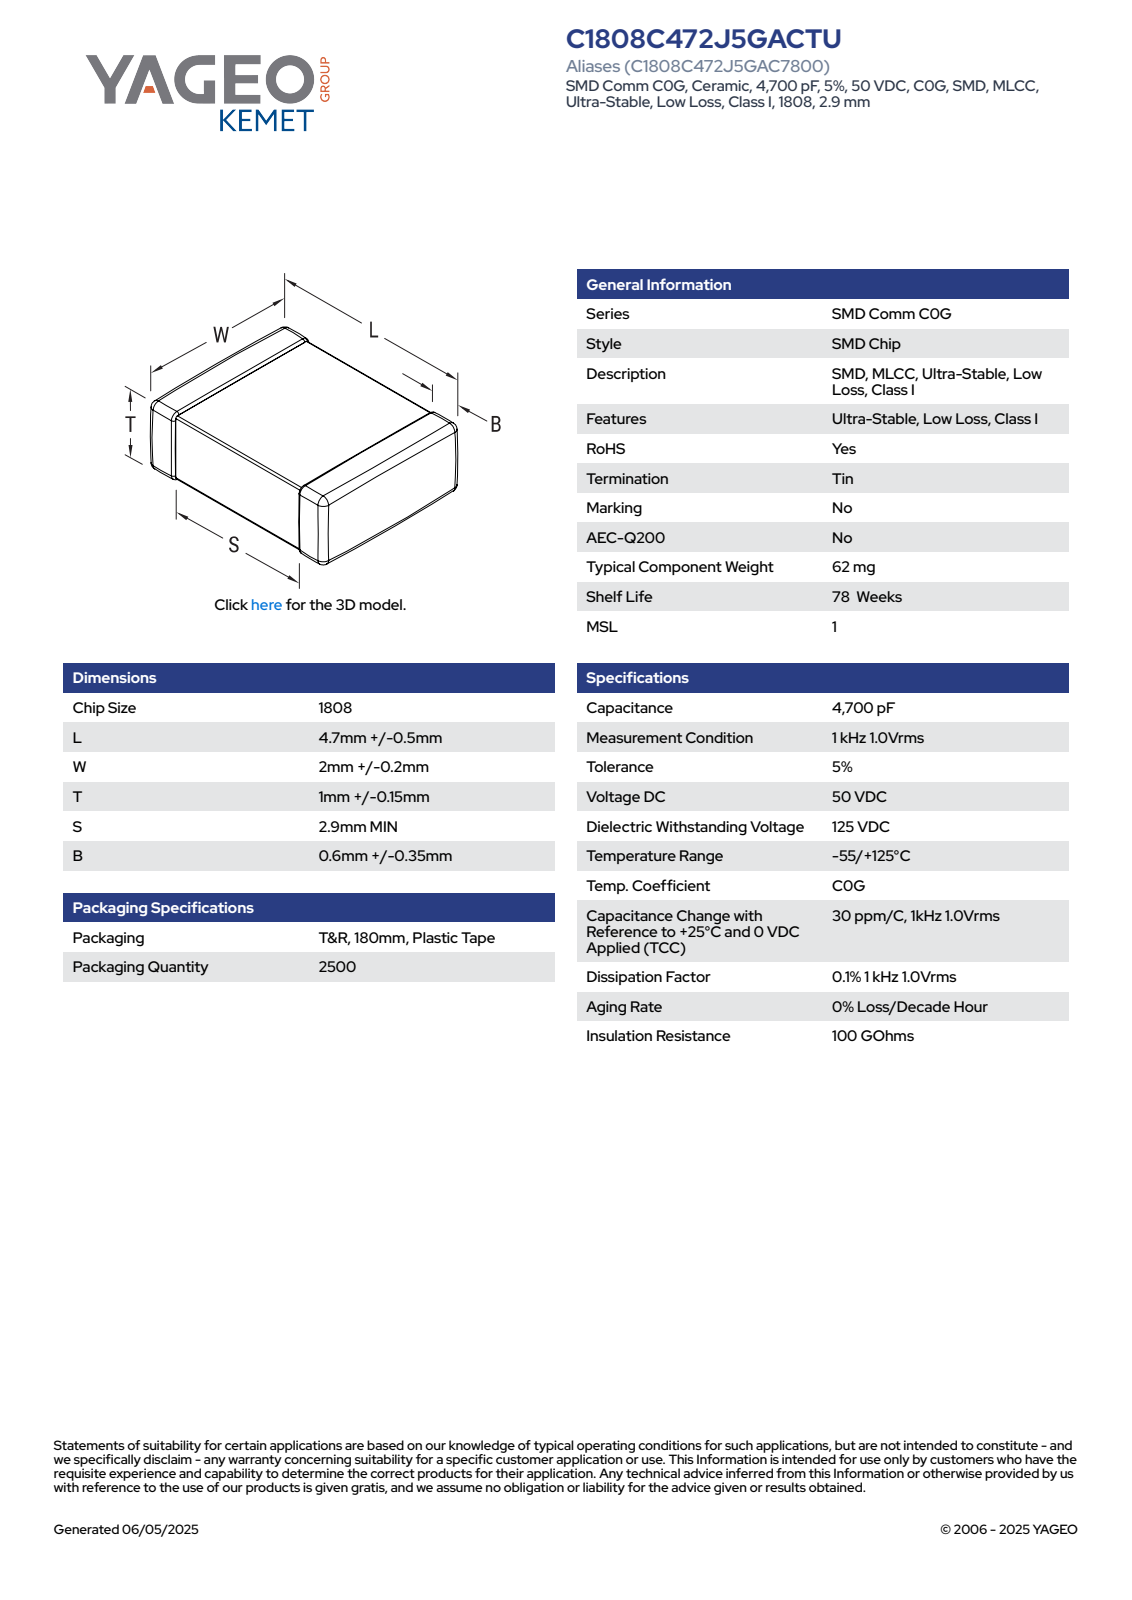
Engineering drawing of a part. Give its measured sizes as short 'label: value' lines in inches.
name: CCS_CCSTD_1808_L5.2W2.2T1.15B0.6
written by: SolidWorks 2021 (AUTOMOTIVE_DESIGN)
unit: in
bodies: 4 solids, 125 faces (71 planar, 38 cylindrical, 16 other)
size: 0.205 × 0.087 × 0.045
volume: 0.001 in³; area: 0.06 in²
face distances: 0.043, 0.041, 0.085, 0.045, 0.083, 0.205, 0.087, 0.044, 0.042, 0.013
